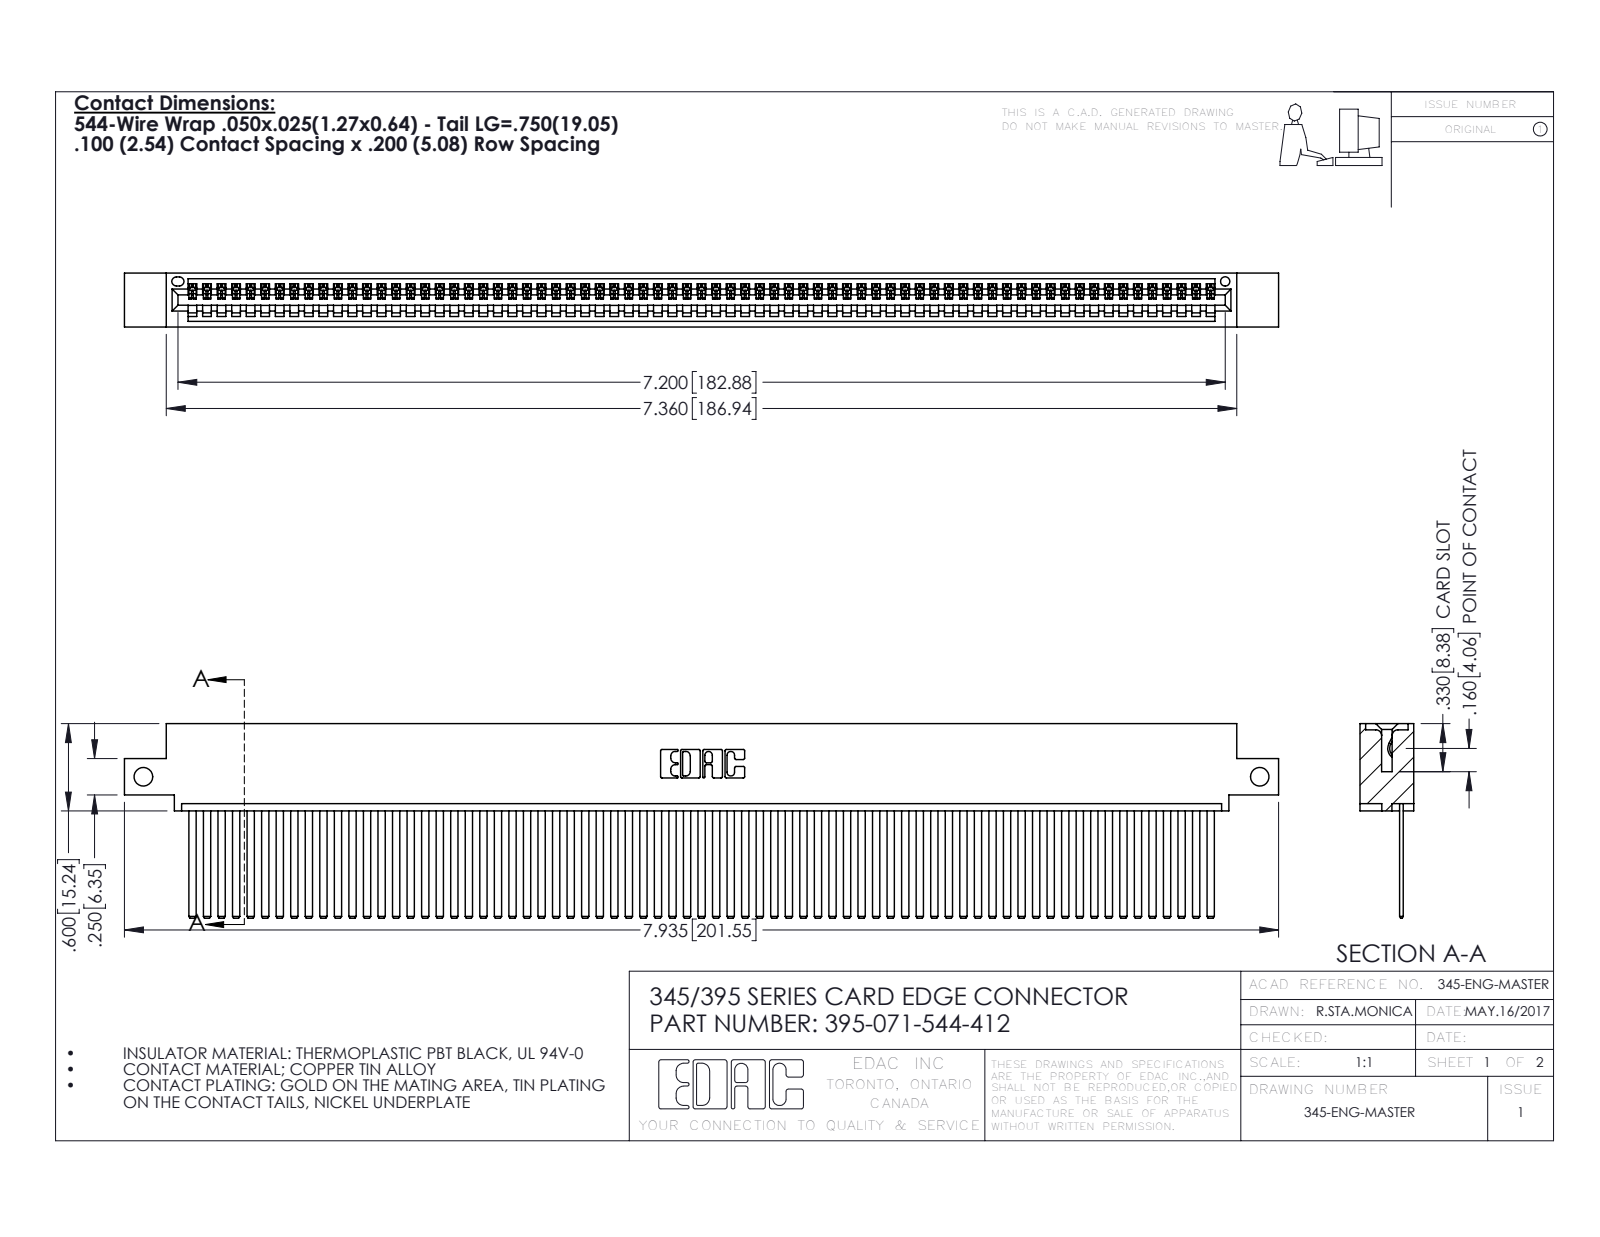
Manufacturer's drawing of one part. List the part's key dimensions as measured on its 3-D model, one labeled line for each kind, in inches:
Part name (STEP PRODUCT): 345 Part_0.110 Offset - Side Mount; 395-071-544-412; 345-292-001_345-293-144
STEP written by: SolidWorks 2016 (CONFIG_CONTROL_DESIGN)
Units: inches
Bodies: 72 solids, 3822 faces (2640 planar, 1182 cylindrical, 0 other)
Overall size (bounding box): 7.935 × 1.337 × 0.37
Volume: 1.223 in³ · Surface area: 45.63 in²
Round holes (diameter × count): ⌀0.128 ×2, ⌀0.064 ×1
Partial cylindrical surfaces — rounded edges, fillets, slot ends (radius × count): R0.006 ×142, R0.01 ×22, R0.007 ×6, R0.031 ×6, R0.026 ×3, R0.031 ×2, R0.04 ×2, R0.014 ×1
Main face-to-face distances: 0.072, 0.298, 0.025, 0.098, 0.272, 0.37, 0.2, 0.225, 0.149, 0.072
Hole centre spacings: 7.675
